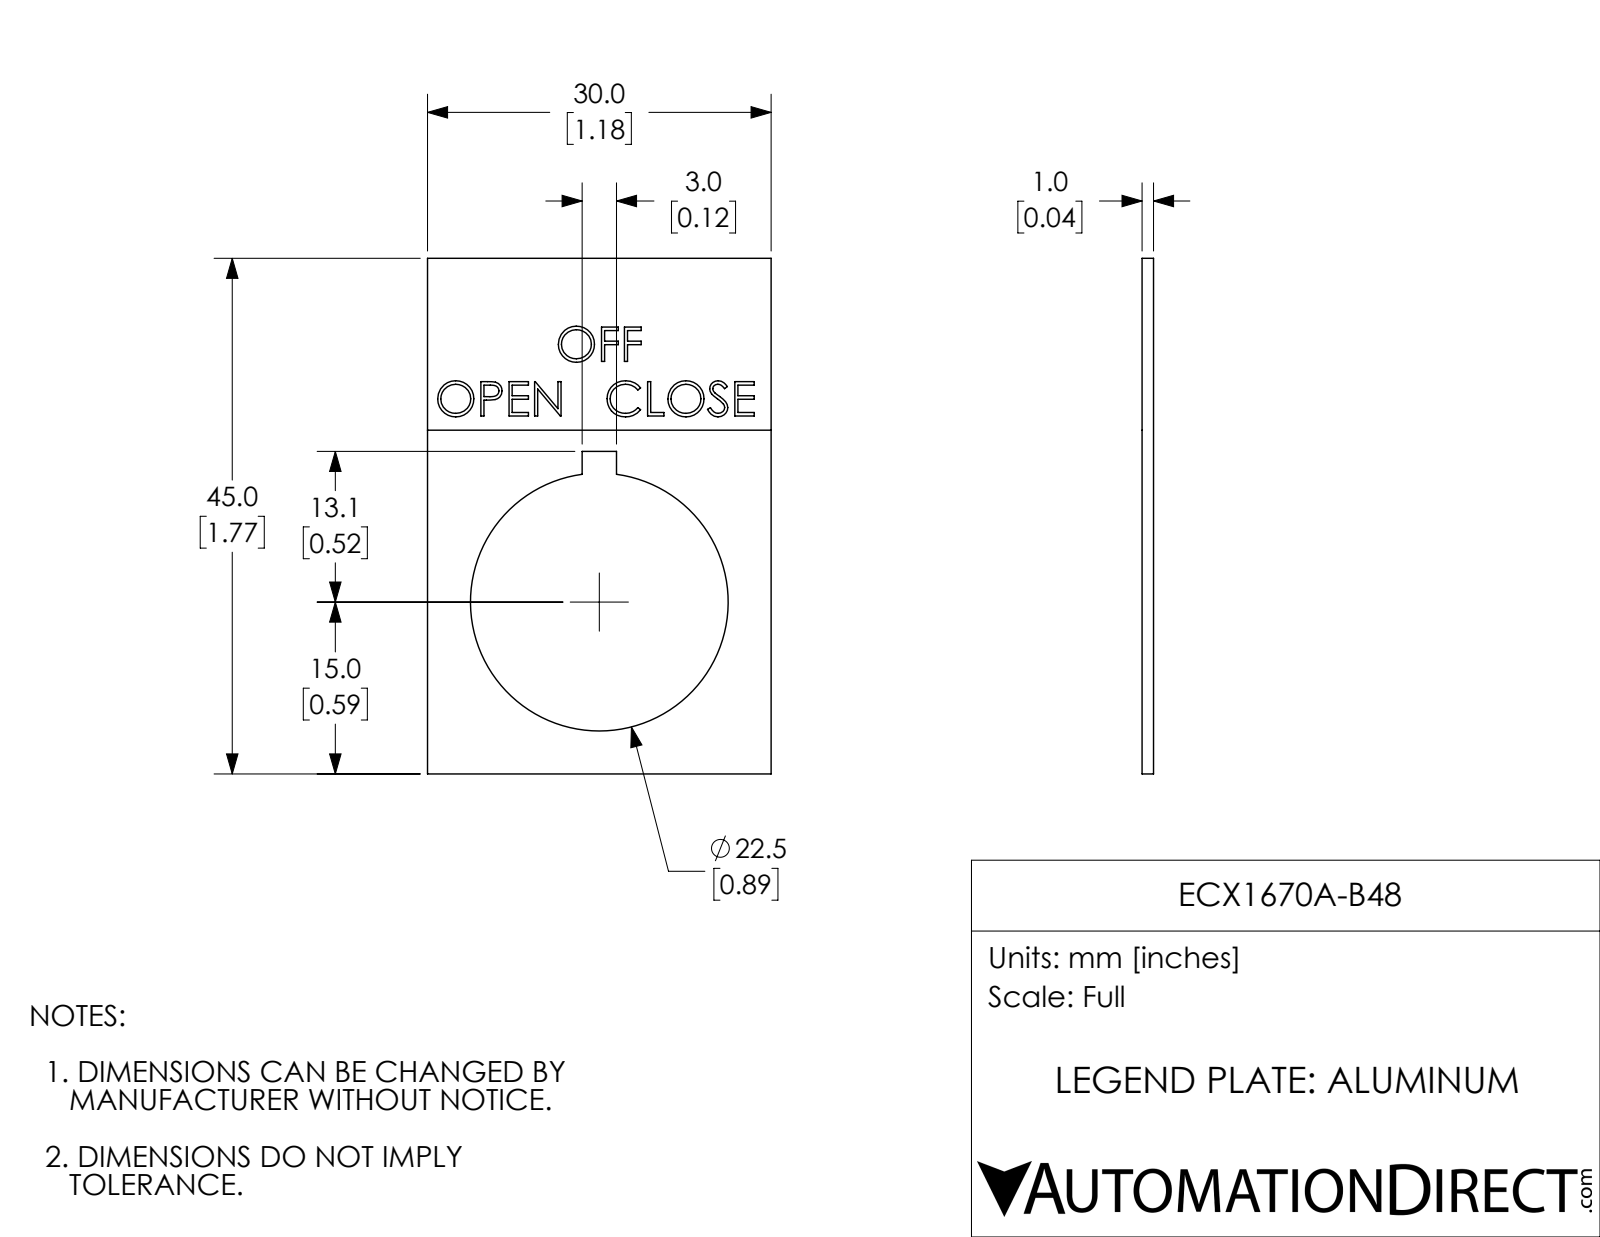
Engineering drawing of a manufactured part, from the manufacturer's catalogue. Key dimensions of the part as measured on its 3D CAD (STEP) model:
Part name (STEP PRODUCT): ECX1670A-B48
STEP written by: SolidWorks 2017 (AUTOMOTIVE_DESIGN)
Units: inches
Bodies: 1 solid, 155 faces (98 planar, 3 cylindrical, 54 other)
Overall size (bounding box): 1.772 × 1.181 × 0.039
Volume: 0.058 in³ · Surface area: 3.29 in²
Round holes (diameter × count): ⌀0.886 ×1
Main face-to-face distances: 0.039, 1.181, 1.772, 0.038, 0.531, 0.65, 1.108, 0.663, 0.118, 0.012
